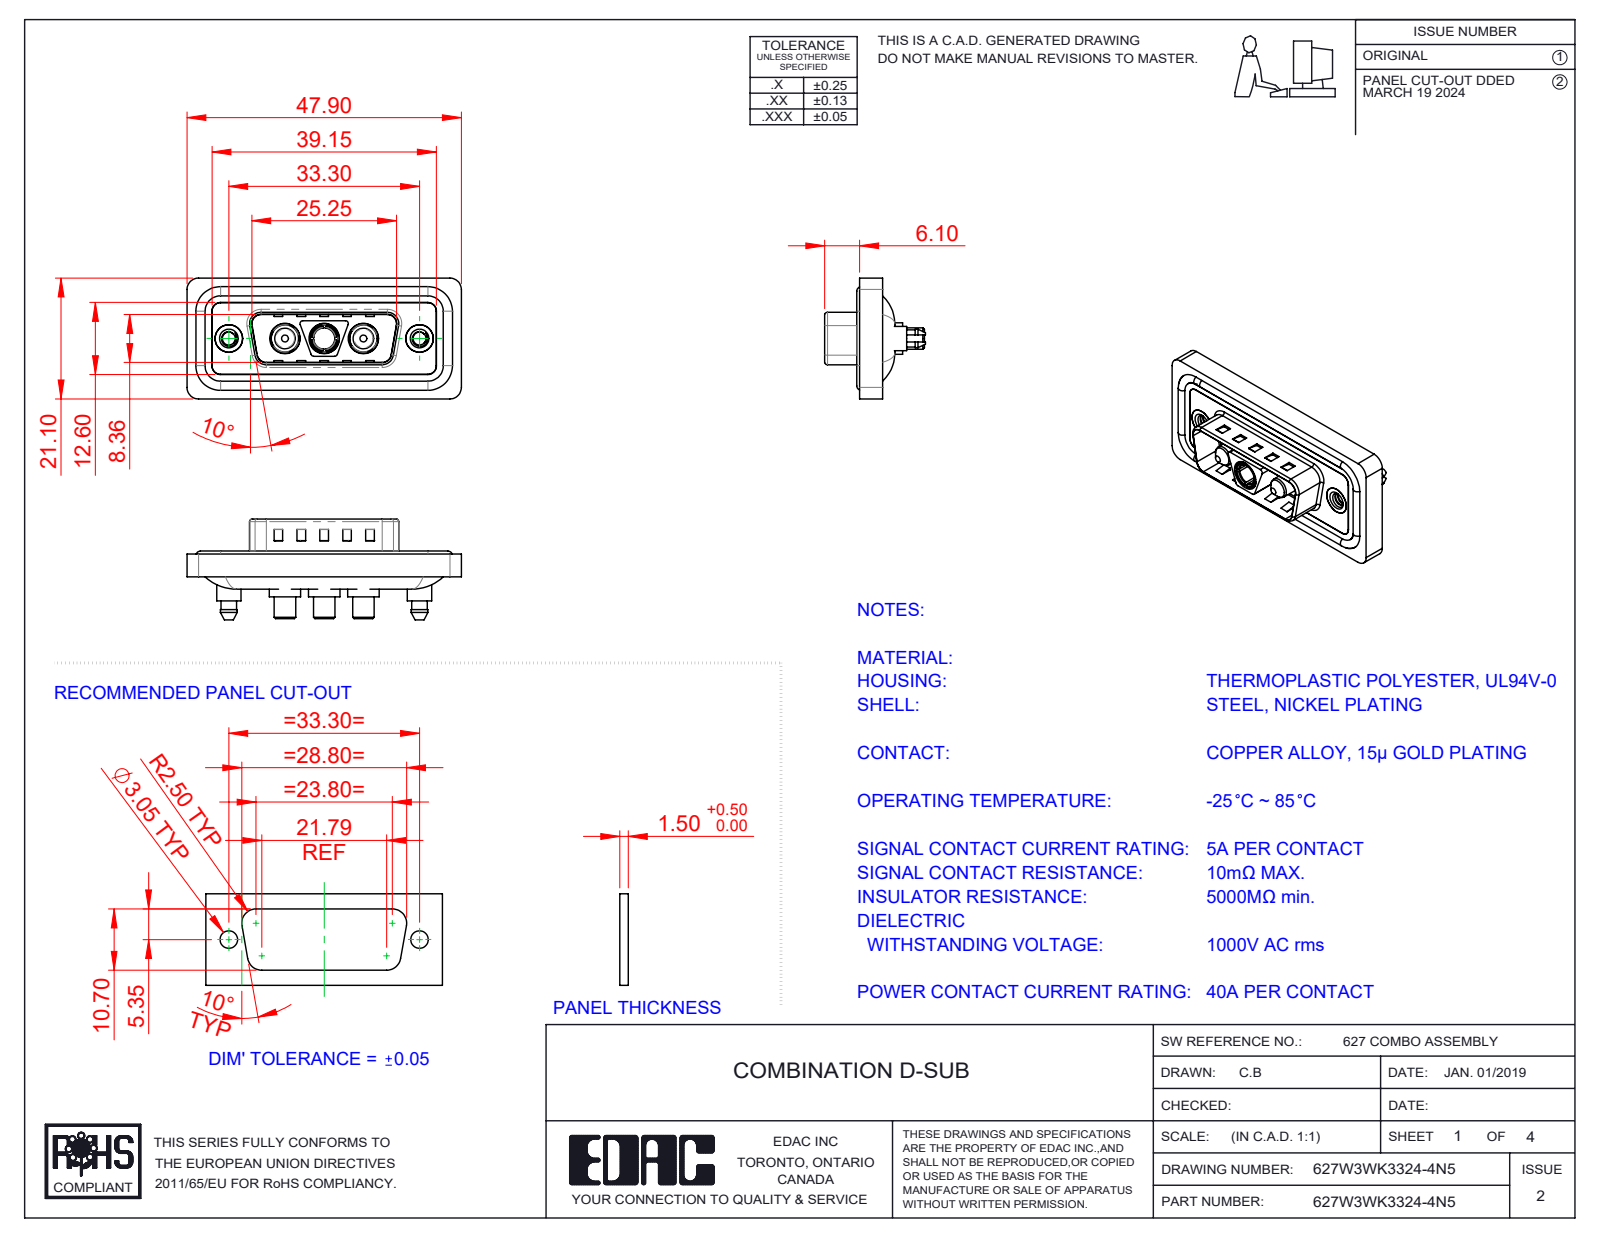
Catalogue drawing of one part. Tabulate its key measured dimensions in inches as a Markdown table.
| quantity | value |
| --- | --- |
| part name | 627Combo Waterproof Housing_15 Contacts; 627Combo Shell Rear_15 Contacts; 627Combo Threaded Boardlock_5; 627Combo Housing_3WK3 (+4 more) |
| STEP written by | SolidWorks 2023 (CONFIG_CONTROL_DESIGN) |
| units | inches |
| bodies | 13 solids, 659 faces (247 planar, 282 cylindrical, 130 other) |
| overall size | 1.886 × 0.831 × 0.693 |
| volume | 0.359 in³ |
| surface area | 14.71 in² |
| round holes (diameter × count) | 0.191 × 3, 0.209 × 3, 0.089 × 2, 0.157 × 2, 0.189 × 2, 0.197 × 2, 0.146 × 1 |
| round bosses / shafts (diameter × count) | 0.063 × 4, 0.217 × 3, 0.205 × 3, 0.187 × 3, 0.148 × 3, 0.213 × 2, 0.193 × 2, 0.167 × 2 |
| partial cylindrical surfaces (radius × count) | 0.059 × 28, 0.079 × 20, 0.02 × 12, 0.063 × 10, 0.01 × 4, 0.024 × 4, 0.026 × 4, 0.035 × 4 |
| main face-to-face distances | 0.016, 0.043, 0.059, 0.122, 0.02, 0.063, 0.114, 0.157, 0.028, 0.032 |
| hole center spacings | 0.27, 0.386, 0.656, 0.925, 0.539, 1.311 |
